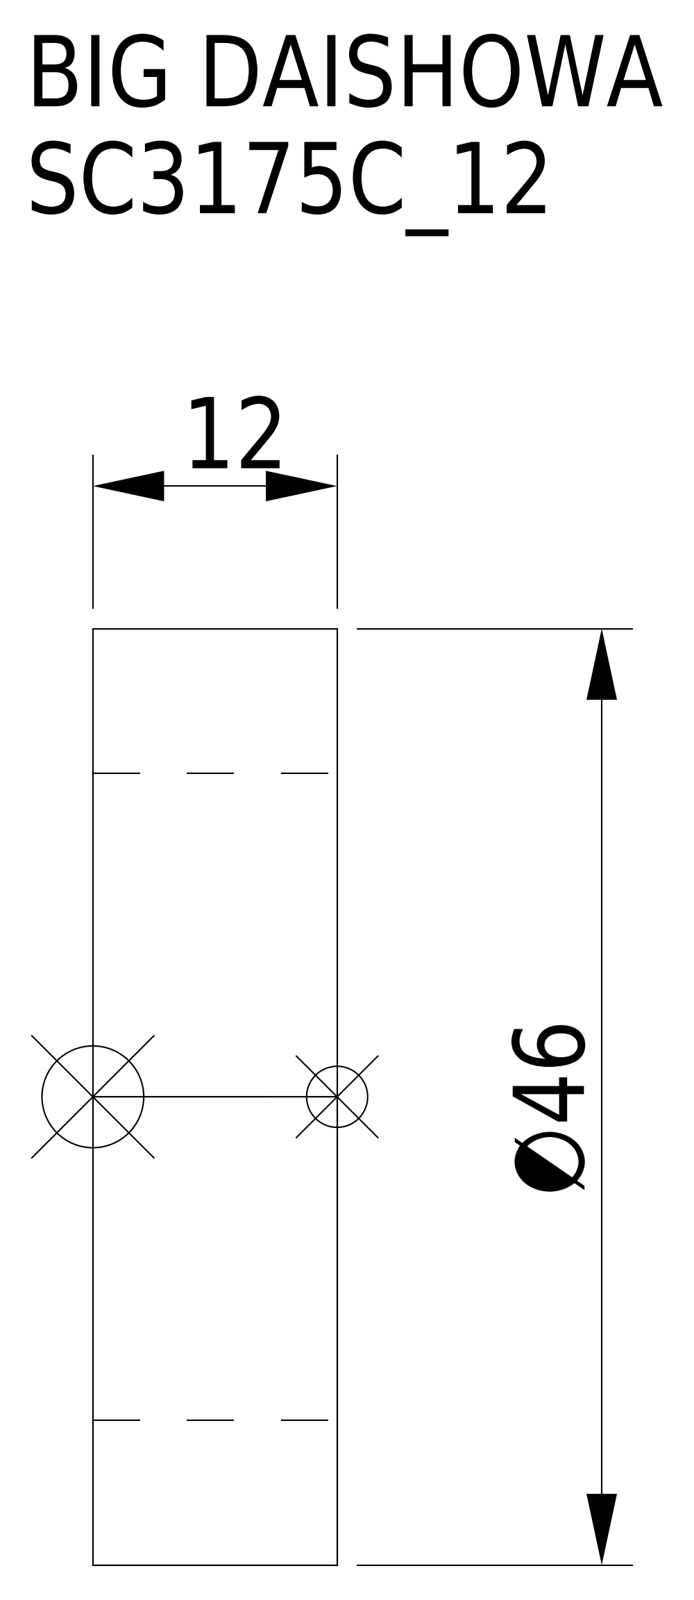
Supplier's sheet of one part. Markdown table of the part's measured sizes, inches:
| quantity | value |
| --- | --- |
| part name | SC3175C_12 |
| STEP written by | CREO PARAMETRIC BY PTC INC, 2016380 (AUTOMOTIVE_DESIGN) |
| units | inches |
| bodies | 1 solid, 8 faces (5 planar, 3 cylindrical, 0 other) |
| overall size | 1.811 × 1.811 × 0.472 |
| volume | 0.616 in³ |
| surface area | 7.296 in² |
| round holes (diameter × count) | 1.25 × 1 |
| round bosses / shafts (diameter × count) | 1.811 × 1 |
| main face-to-face distances | 0.472, 0.319 |
